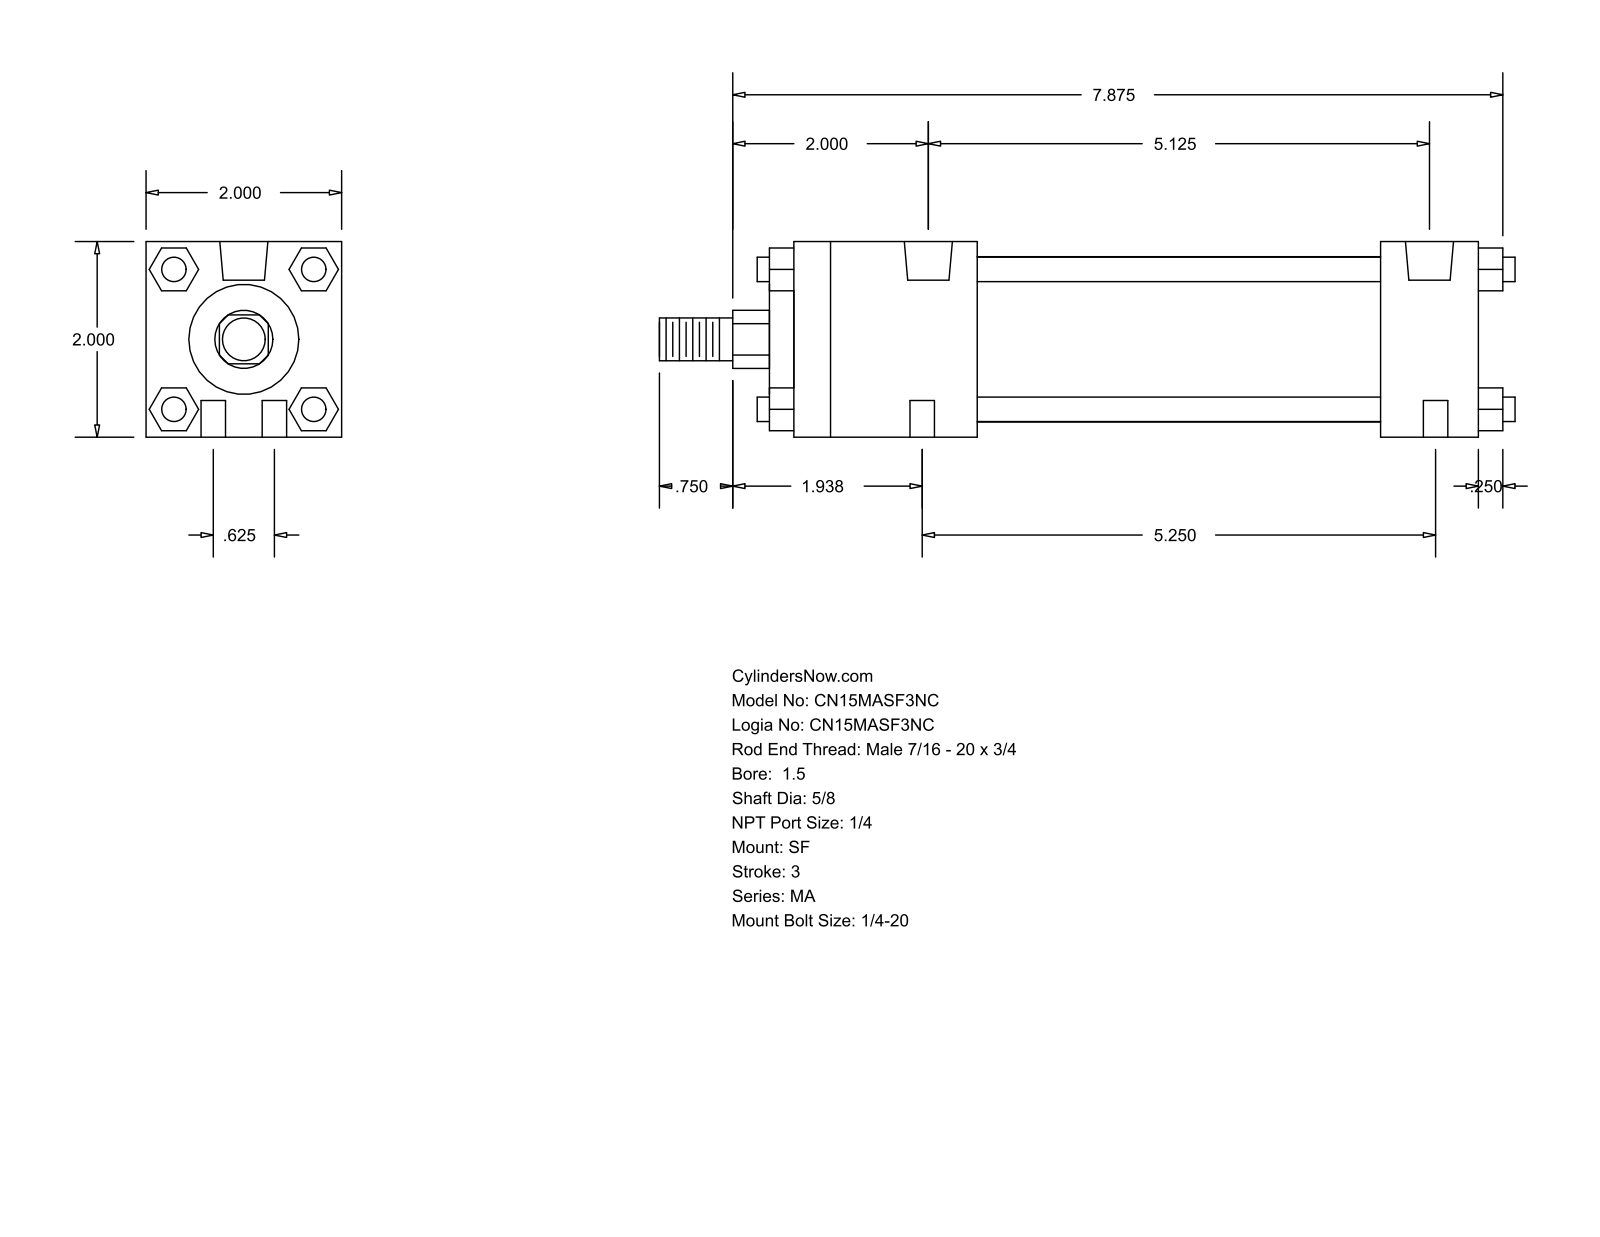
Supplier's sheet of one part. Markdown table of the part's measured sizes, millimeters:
| quantity | value |
| --- | --- |
| part name | MA_SF__0150_0.625 |
| STEP written by | GSSL Pune (CONFIG_CONTROL_DESIGN) |
| units | millimeters |
| bodies | 0 solids, 124 faces (94 planar, 30 cylindrical, 0 other) |
| overall size | 222.25 × 50.8 × 50.8 |
| round holes (diameter × count) | 6.35 × 4, 7.94 × 2, 12.49 × 2 |
| round bosses / shafts (diameter × count) | 6.35 × 4, 42.93 × 1, 28.57 × 1, 15.88 × 1, 11.11 × 1 |
| partial cylindrical surfaces (radius × count) | 7.54 × 1 |
| main face-to-face distances | 50.8, 177.8, 6.35, 25.4, 184.15, 47.62, 152.4, 104.78, 130.18, 53.97 |
| hole center spacings | 8.1, 132, 15.88, 130.17, 133.35, 134.29 |
